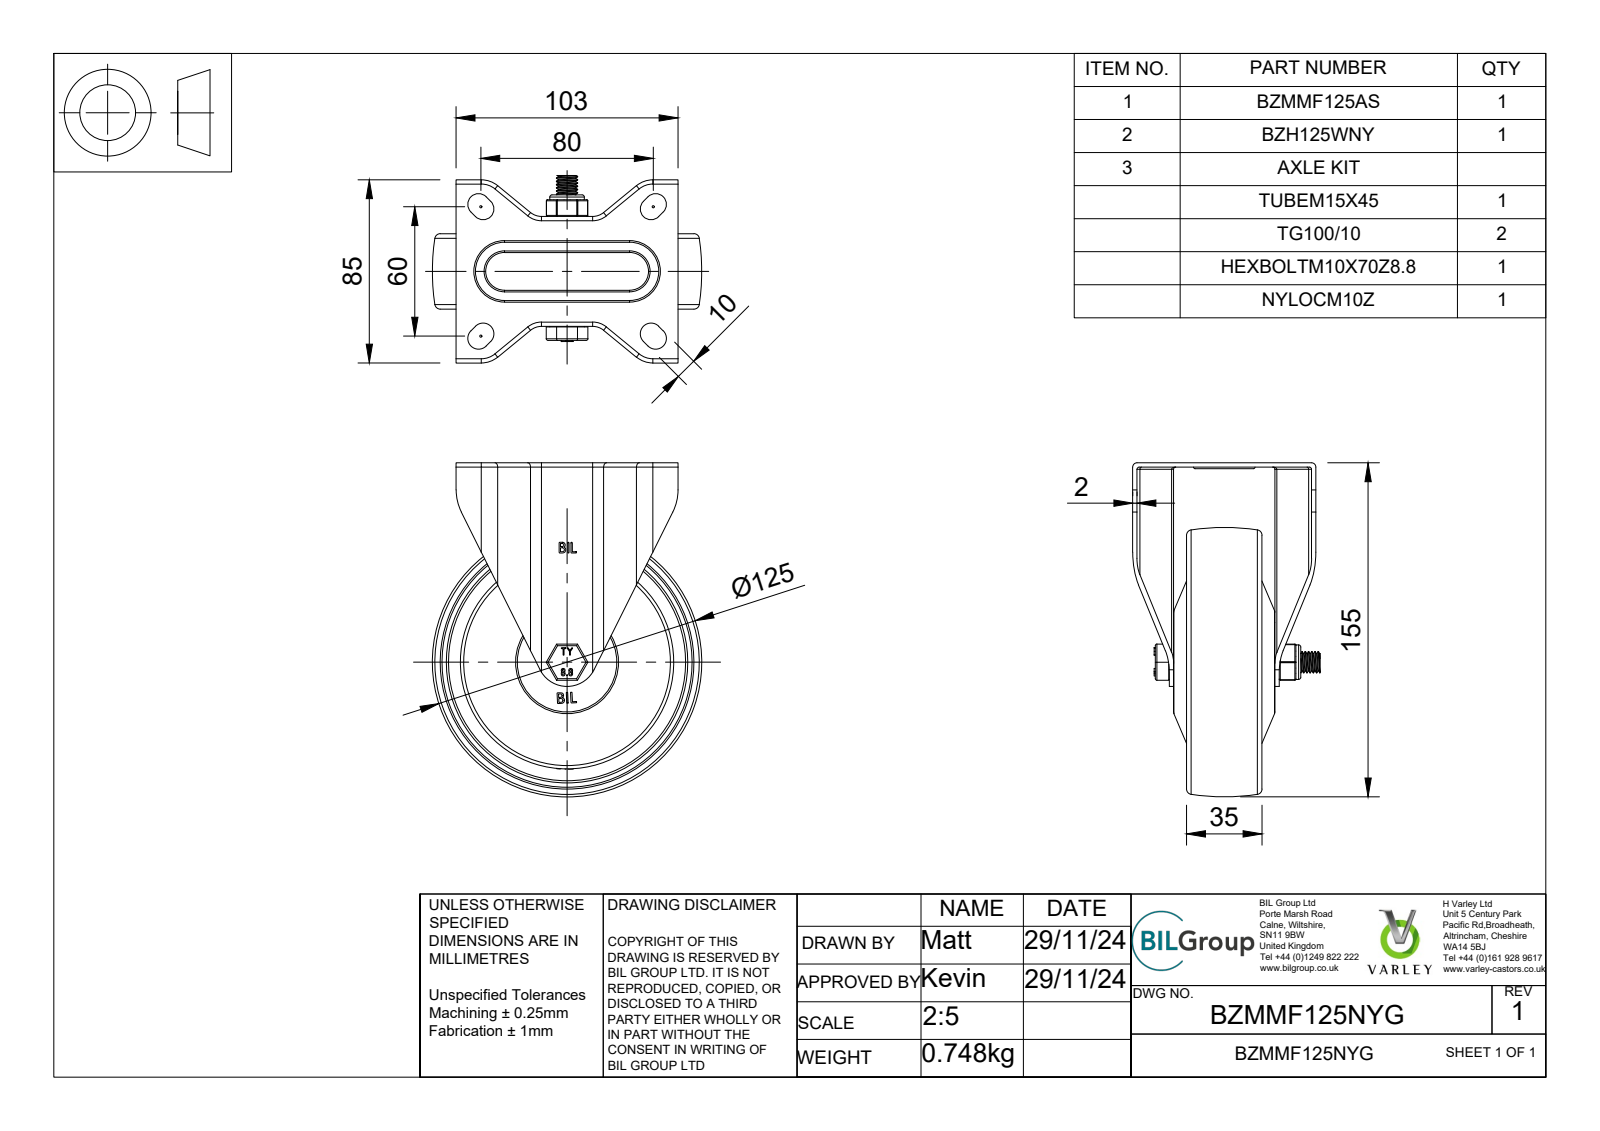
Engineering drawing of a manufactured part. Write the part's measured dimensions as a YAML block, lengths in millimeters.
part_name: "BZMMF125NYG v4; BZMMF125AS - 47 v2; ZINC PLATED, PRESSED STEEL BRACKET; BZH125WNY v1 (+8 more)"
step_written_by: "Autodesk Translation Framework v13.20.0.188 (AP242_MANAGED_MODEL_BASED_3D_ENGINEERING_MIM_LF)"
units: millimeters
bodies: {solids: 8, faces: 717, planar: 264, cylindrical: 143, other: 310}
overall_size: [155, 125, 87]
volume: 232419
surface_area: 141966
round_holes:
  - {diameter: 10, count: 1}
  - {diameter: 10.2, count: 1}
  - {diameter: 10.5, count: 1}
  - {diameter: 12, count: 1}
  - {diameter: 15.2, count: 1}
  - {diameter: 98, count: 1}
  - {diameter: 112, count: 1}
round_bosses_or_shafts:
  - {diameter: 99, count: 1}
  - {diameter: 16, count: 1}
  - {diameter: 14.95, count: 1}
  - {diameter: 9.85, count: 1}
  - {diameter: 8.14, count: 1}
partial_cylinders:
  - {radius: 0.5, count: 18}
  - {radius: 0.75, count: 14}
  - {radius: 1, count: 8}
  - {radius: 2, count: 8}
  - {radius: 5, count: 8}
  - {radius: 4, count: 4}
  - {radius: 6, count: 4}
  - {radius: 8, count: 4}
face_to_face_distances: [2, 20.25, 26.75, 18.84, 28.75, 22.25, 49, 6.5, 47, 2.5]
